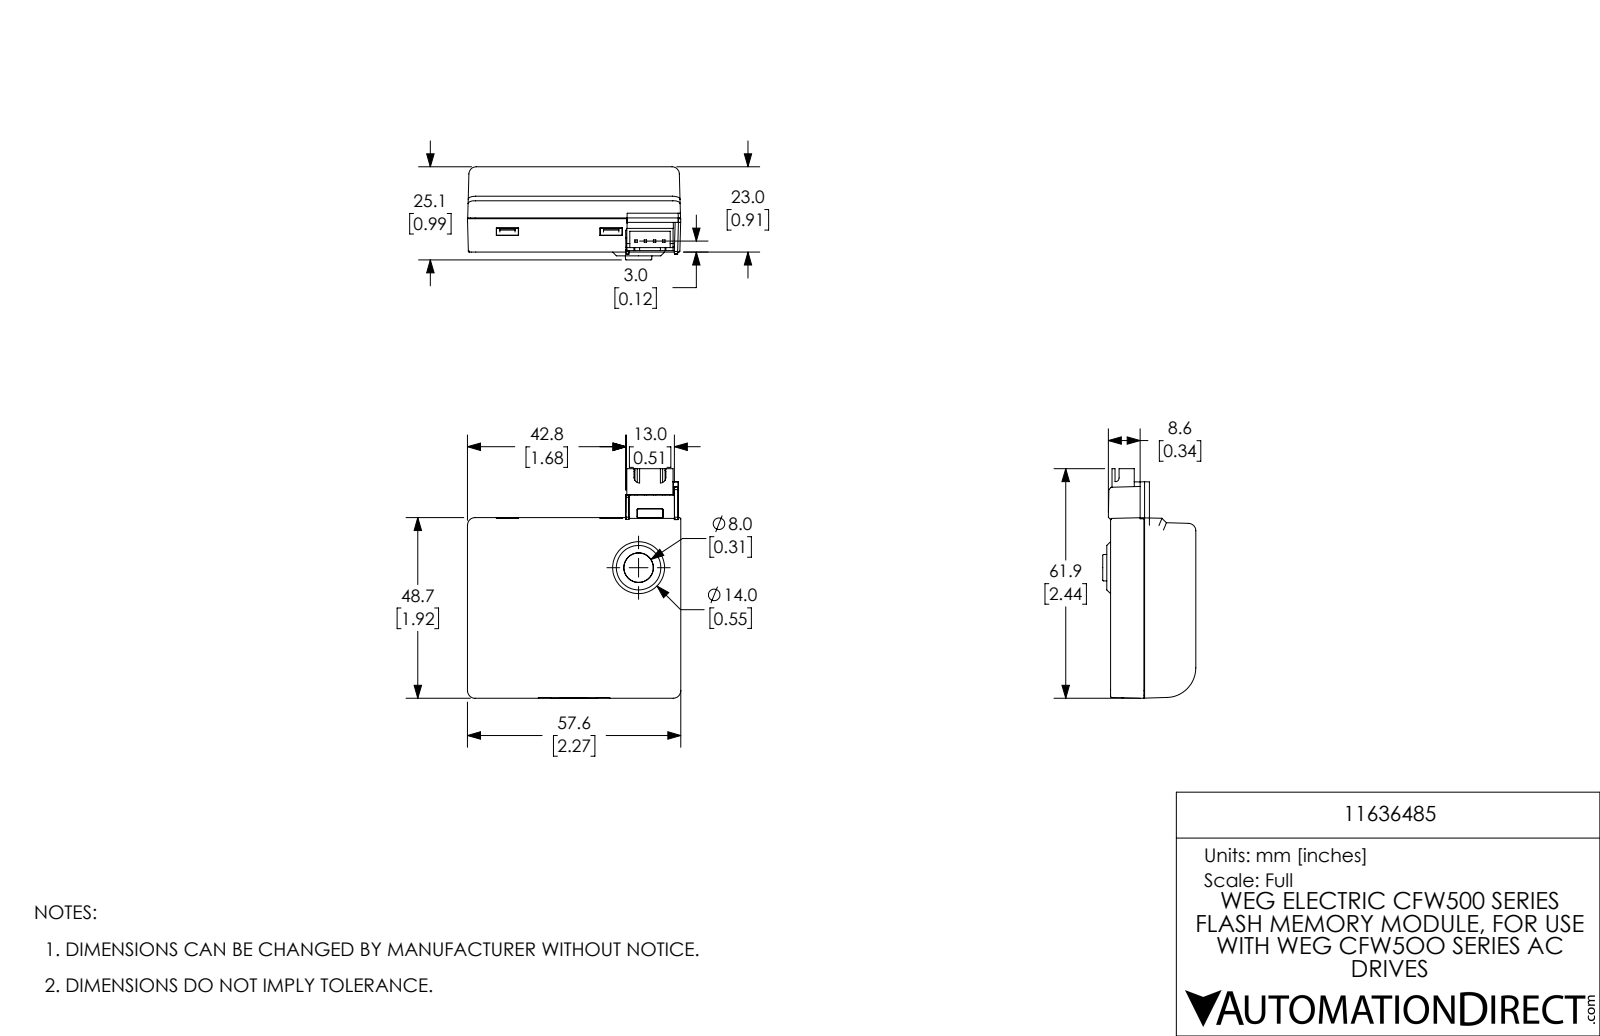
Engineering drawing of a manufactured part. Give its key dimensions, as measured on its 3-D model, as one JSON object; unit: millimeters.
{"part_name": "11636485_ MODULO MEMORIA CFW500_MMF nc", "step_written_by": "SolidWorks 2017 (AUTOMOTIVE_DESIGN)", "units": "millimeters", "bodies": {"solids": 5, "faces": 459, "planar": 323, "cylindrical": 86, "other": 50}, "overall_size": [61.9, 57.6, 25.1], "volume_mm3": 68860, "surface_area_mm2": 18760, "round_bosses_or_shafts": [[1.7, 4]], "partial_cylinders_radius": [[2, 14], [0.3, 9], [0.1, 8], [0.5, 2], [1.5, 2], [1.7, 2], [0.5, 1], [1, 1]], "face_to_face_distances": [9, 2, 7, 14, 16, 23, 57.5, 48.7, 1, 0.6]}
